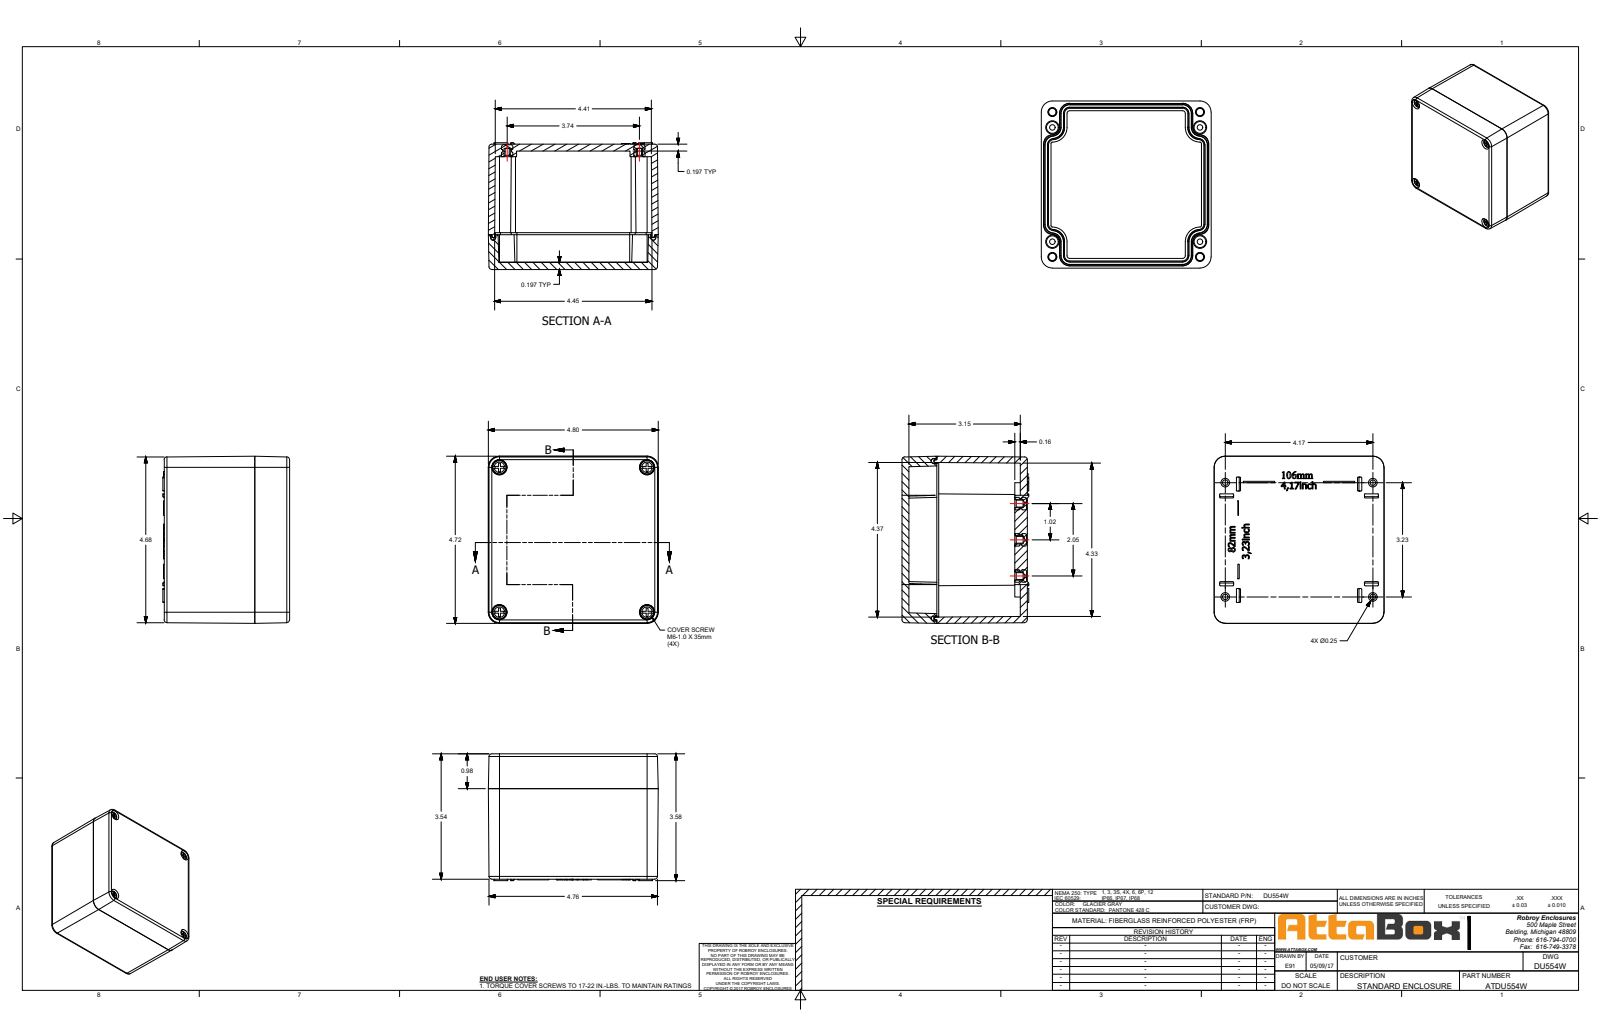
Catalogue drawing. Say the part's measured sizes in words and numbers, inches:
The part is named "DU554W". Its 3-D file was written by "SolidWorks 2018 (AUTOMOTIVE_DESIGN)". It is 17 solids with 1312 faces: 657 planar, 174 cylindrical and 481 other. Overall it measures 4.803 by 4.724 by 3.583 inches. Its volume is 23.98 cubic inches and its surface area 264.4 square inches. Round holes: 10 of diameter 0.194, 6 of diameter 0.236, 4 of diameter 0.213, 4 of diameter 0.276. Round bosses or shafts: 10 of diameter 0.291, 4 of diameter 0.374, 4 of diameter 0.315, 4 of diameter 0.236, 4 of diameter 0.205. Partial cylindrical surfaces (rounded edges, fillets, slot ends): 32 of radius 0.02, 12 of radius 0.069, 8 of radius 0.148, 8 of radius 0.285, 6 of radius 0.016, 4 of radius 0.078, 4 of radius 0.079, 4 of radius 0.108. The main face-to-face distances are 3.346, 0.197, 0.177, 3.543, 3.15, 0.984, 2.362, 0.787, 2.559, 0.453. The hole center spacings are 1.024, 1.046, 2.059, 3.078, 3.878, 4.087, 4.455, 5.009.
